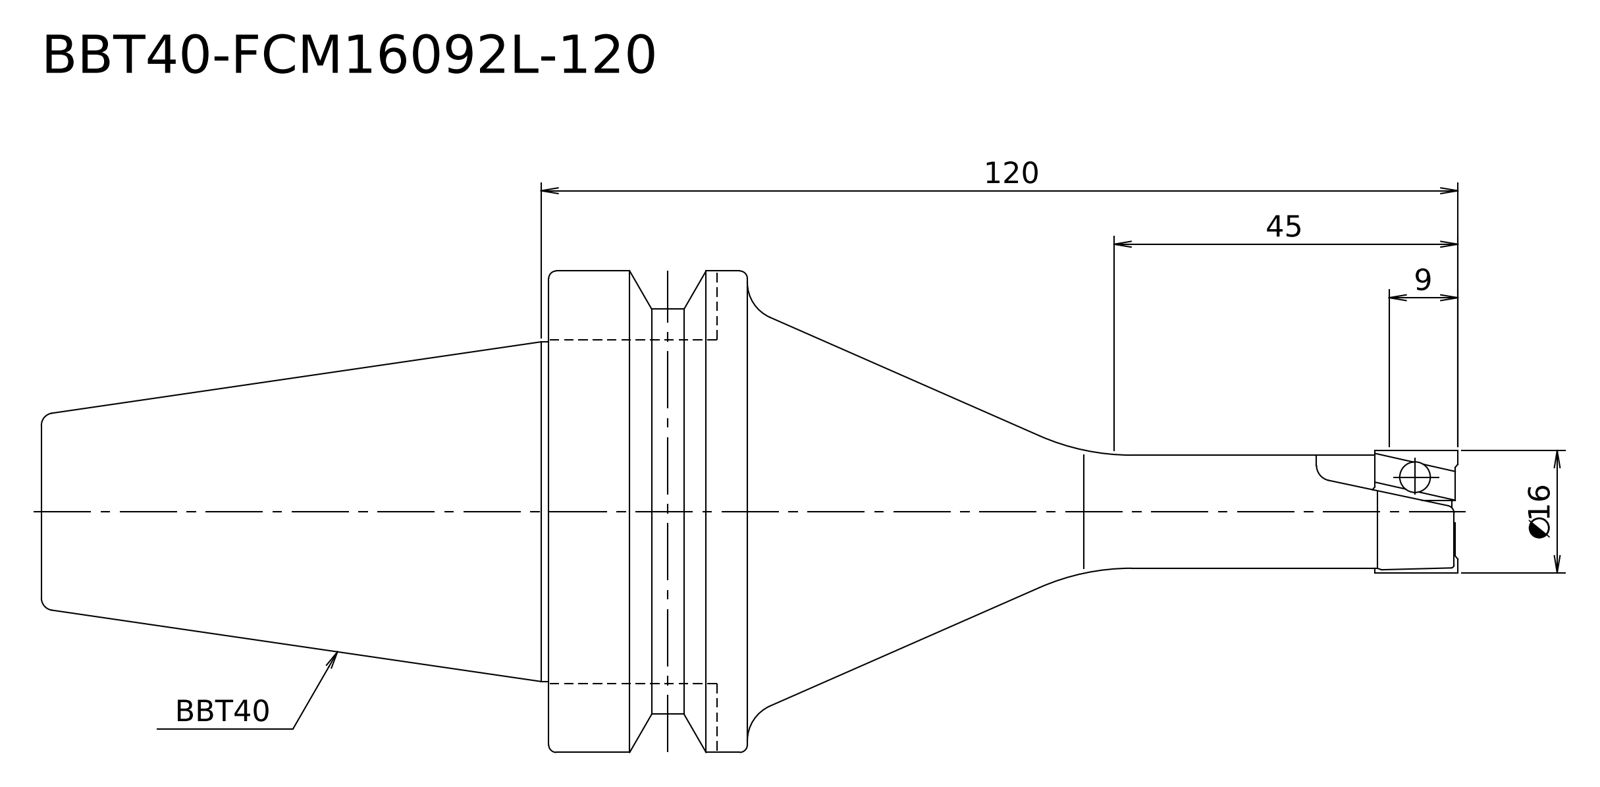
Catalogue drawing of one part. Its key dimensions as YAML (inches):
step_written_by: "Kubotek KeyCreator V8.5.1 (14335) (CONFIG_CONTROL_DESIGN)"
units: inches
bodies: {solids: 1, faces: 17, planar: 4, cylindrical: 6, other: 7}
overall_size: [7.299, 2.48, 2.48]
volume: 11.88
surface_area: 36.97
round_bosses_or_shafts:
  - {diameter: 2.48, count: 1}
  - {diameter: 2.087, count: 1}
  - {diameter: 1.75, count: 1}
  - {diameter: 0.63, count: 1}
  - {diameter: 0.583, count: 1}
face_to_face_distances: [2.614, 1.024, 3.638, 3.661, 4.685, 7.299]
